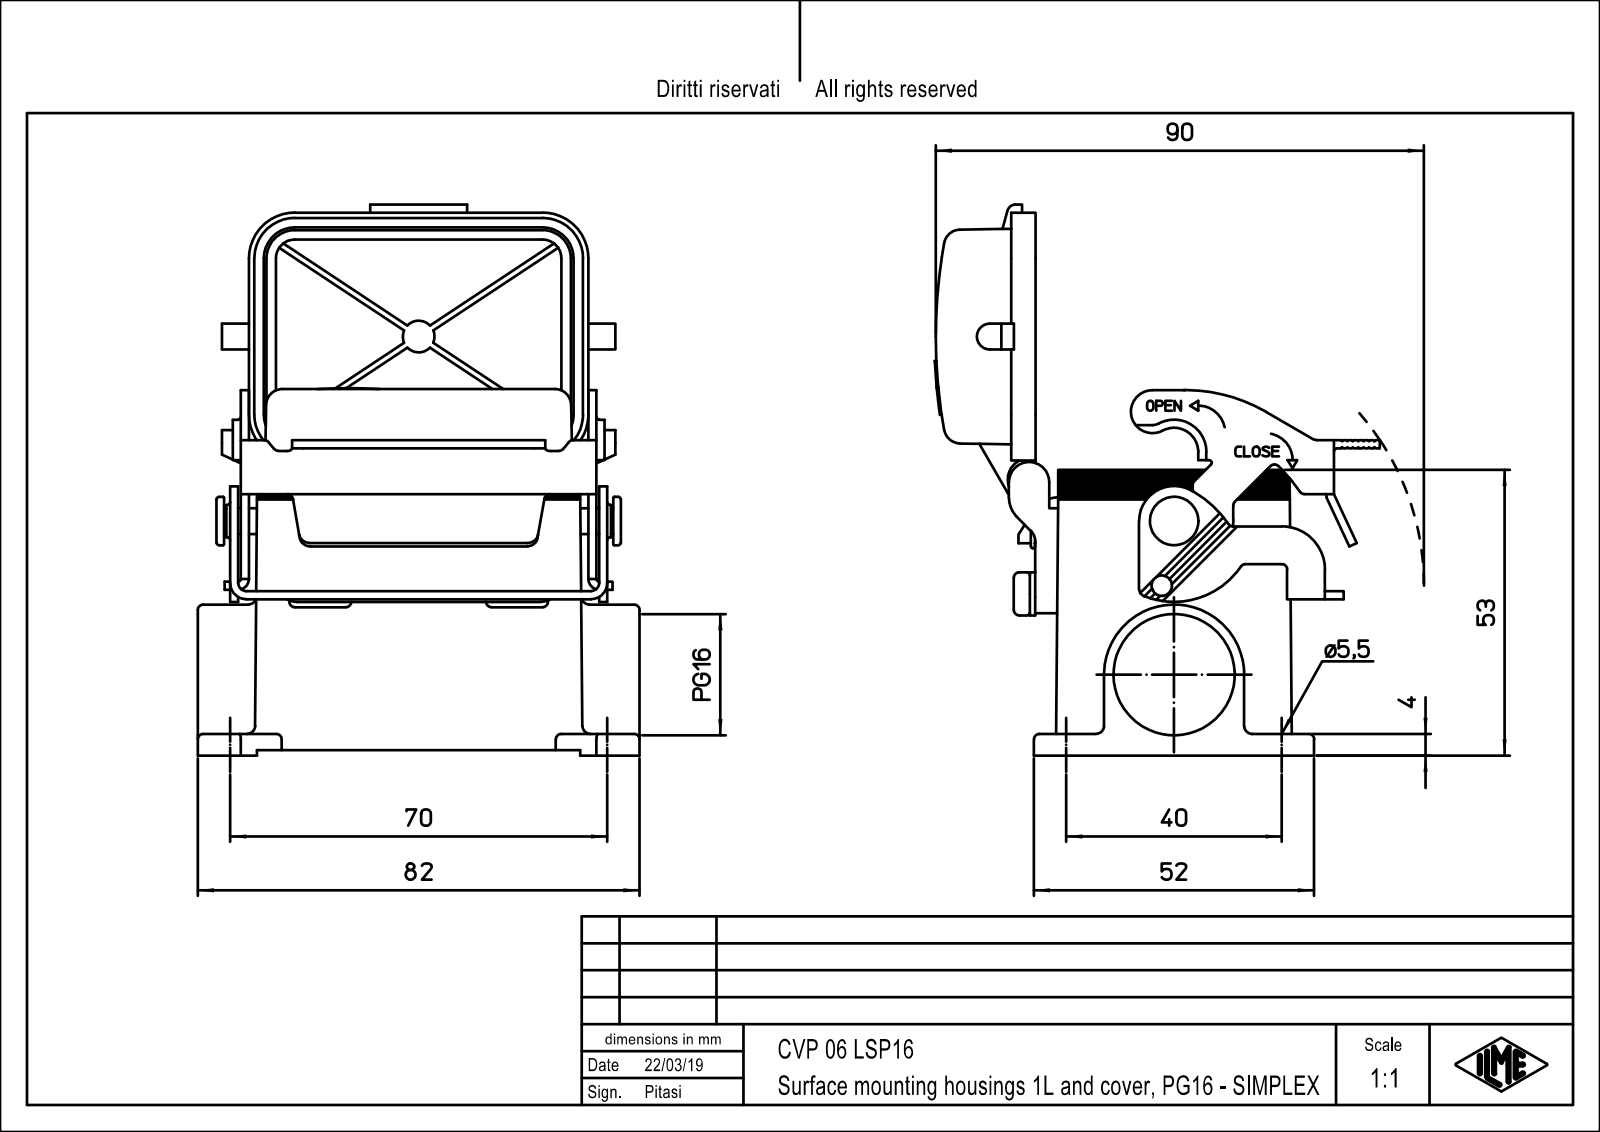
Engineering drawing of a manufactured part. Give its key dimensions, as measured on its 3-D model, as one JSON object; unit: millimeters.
{"part_name": "CVP_06_LSP16.stp", "step_written_by": "PTC Creo Elements/Direct Modeling 19.0E 27-Jun-2016 (C) Parametric Technology GmbH (AUTOMOTIVE_DESIGN)", "units": "millimeters", "bodies": {"solids": 1, "faces": 605, "planar": 384, "cylindrical": 197, "other": 24}, "overall_size": [102.72, 82, 79.7], "volume_mm3": 85736, "surface_area_mm2": 53379, "round_holes": [[2.46, 4], [3, 4], [5.5, 4], [20, 1], [22.5, 1]], "round_bosses_or_shafts": [[0.8, 3], [9, 1], [8.4, 1], [8, 1], [6, 1], [5, 1], [2.4, 1]], "partial_cylinders_radius": [[2, 18], [3, 15], [1.5, 8], [3.5, 7], [1, 5], [6, 5], [0.5, 4], [1.8, 4]], "face_to_face_distances": [4, 40.5, 1.5, 2, 47.75, 44.5, 36.5, 8, 14.5, 43.75], "hole_center_spacings": [14.53, 35.93, 57.37, 66.12, 27, 40, 44, 51.62]}
